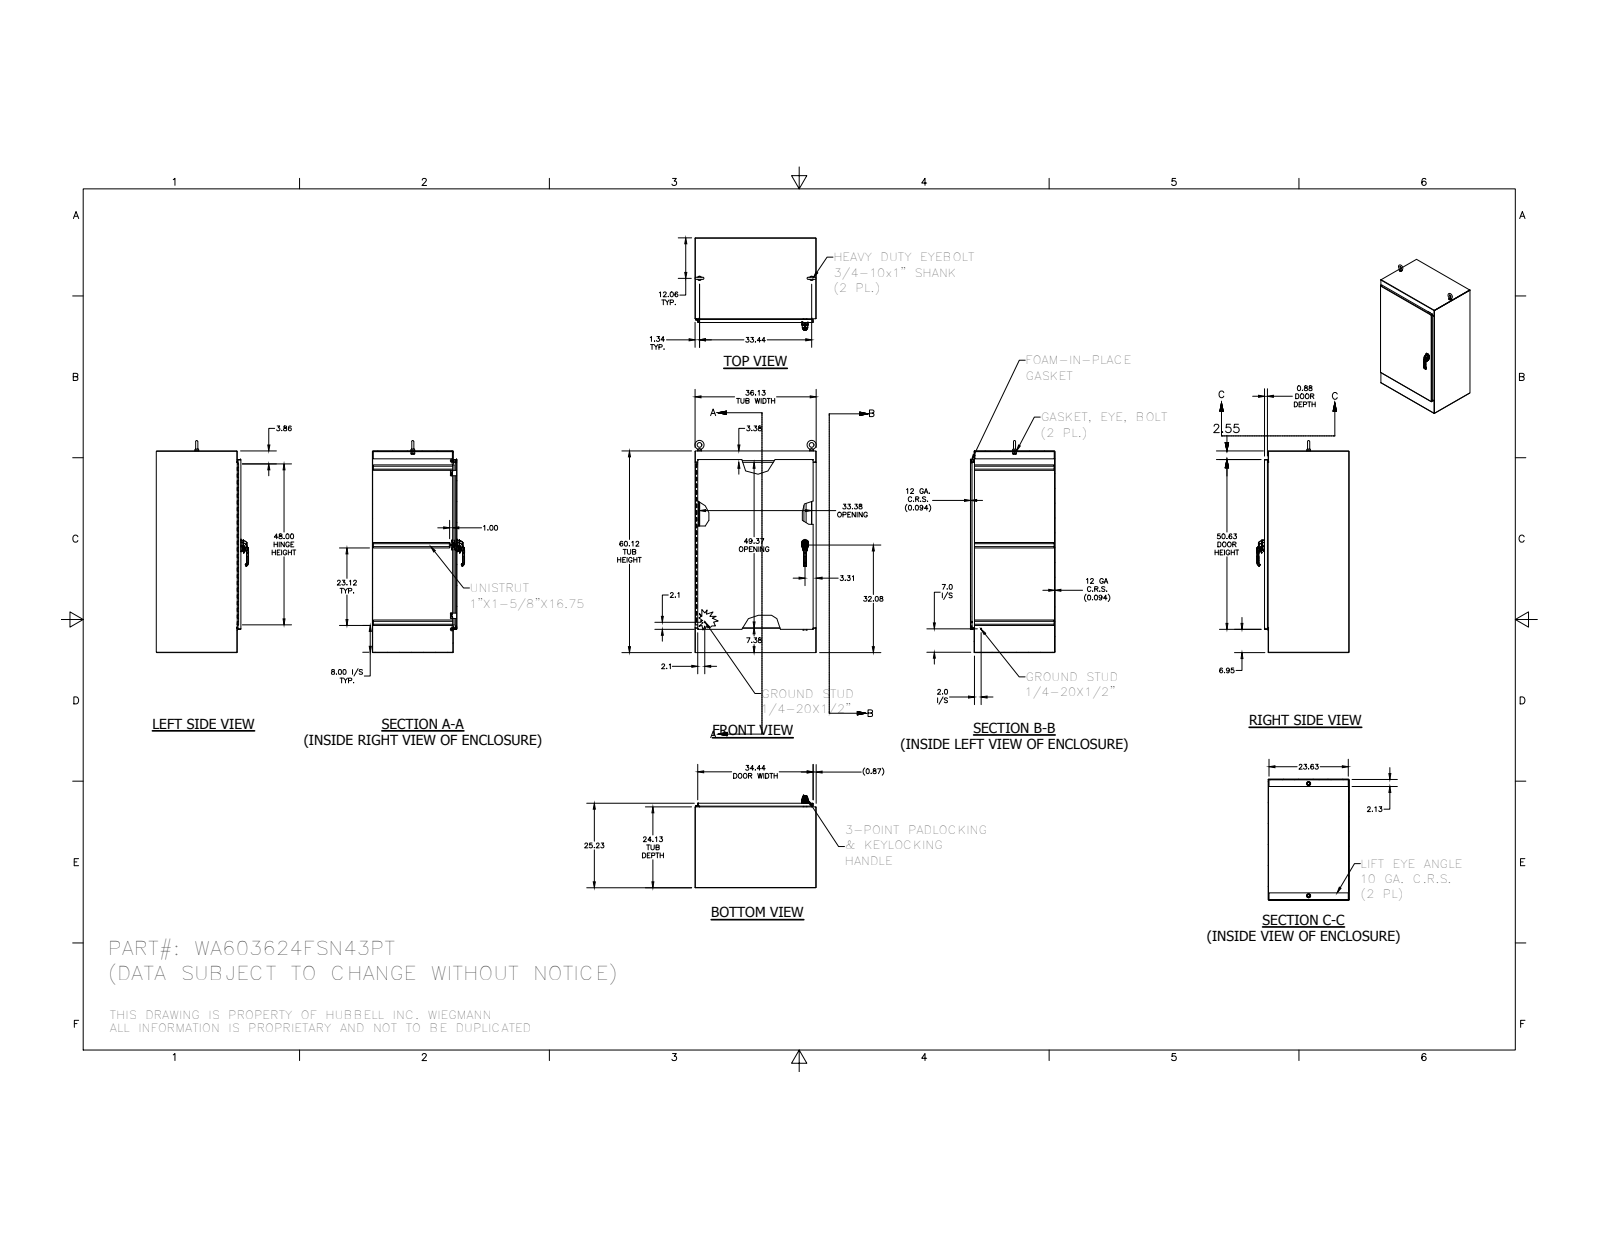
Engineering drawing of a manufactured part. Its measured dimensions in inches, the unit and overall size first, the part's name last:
Units: inches
Overall size (bounding box): 63.248 × 36.125 × 25.227
Round holes (diameter × count): ⌀0.277 ×8, ⌀0.375 ×8, ⌀0.2 ×4, ⌀0.28 ×3, ⌀0.241 ×2, ⌀0.25 ×2, ⌀0.252 ×2, ⌀0.4 ×2, ⌀0.407 ×2, ⌀0.45 ×2, ⌀0.642 ×2, ⌀0.813 ×2
Round bosses / shafts (diameter × count): ⌀1.25 ×2, ⌀1.12 ×2, ⌀1 ×2, ⌀0.75 ×2, ⌀0.563 ×2, ⌀0.527 ×2, ⌀0.5 ×2, ⌀0.375 ×2
Partial cylindrical surfaces — rounded edges, fillets, slot ends (radius × count): R0.01 ×16, R0.031 ×16, R0.125 ×16, R0.05 ×14, R0.125 ×14, R0.019 ×12, R0.053 ×12, R0.086 ×12
Main face-to-face distances: 0.094, 25.133, 36.031, 25.039, 25.227, 60.031, 35.938, 36.125, 24.031, 1.102
Hole centre spacings: 5.333, 16, 10.667, 21.333, 0.762, 0.764, 1.195, 1.272
Volume: 1 022 in³ · Surface area: 21 176 in²
Bodies: 51 solids, 1632 faces (694 planar, 618 cylindrical, 320 other)
Part name (STEP PRODUCT): HFW31712; HFW3681; HFW3121; 3063 (+8 more)
STEP written by: SolidWorks 2014 (AUTOMOTIVE_DESIGN)
